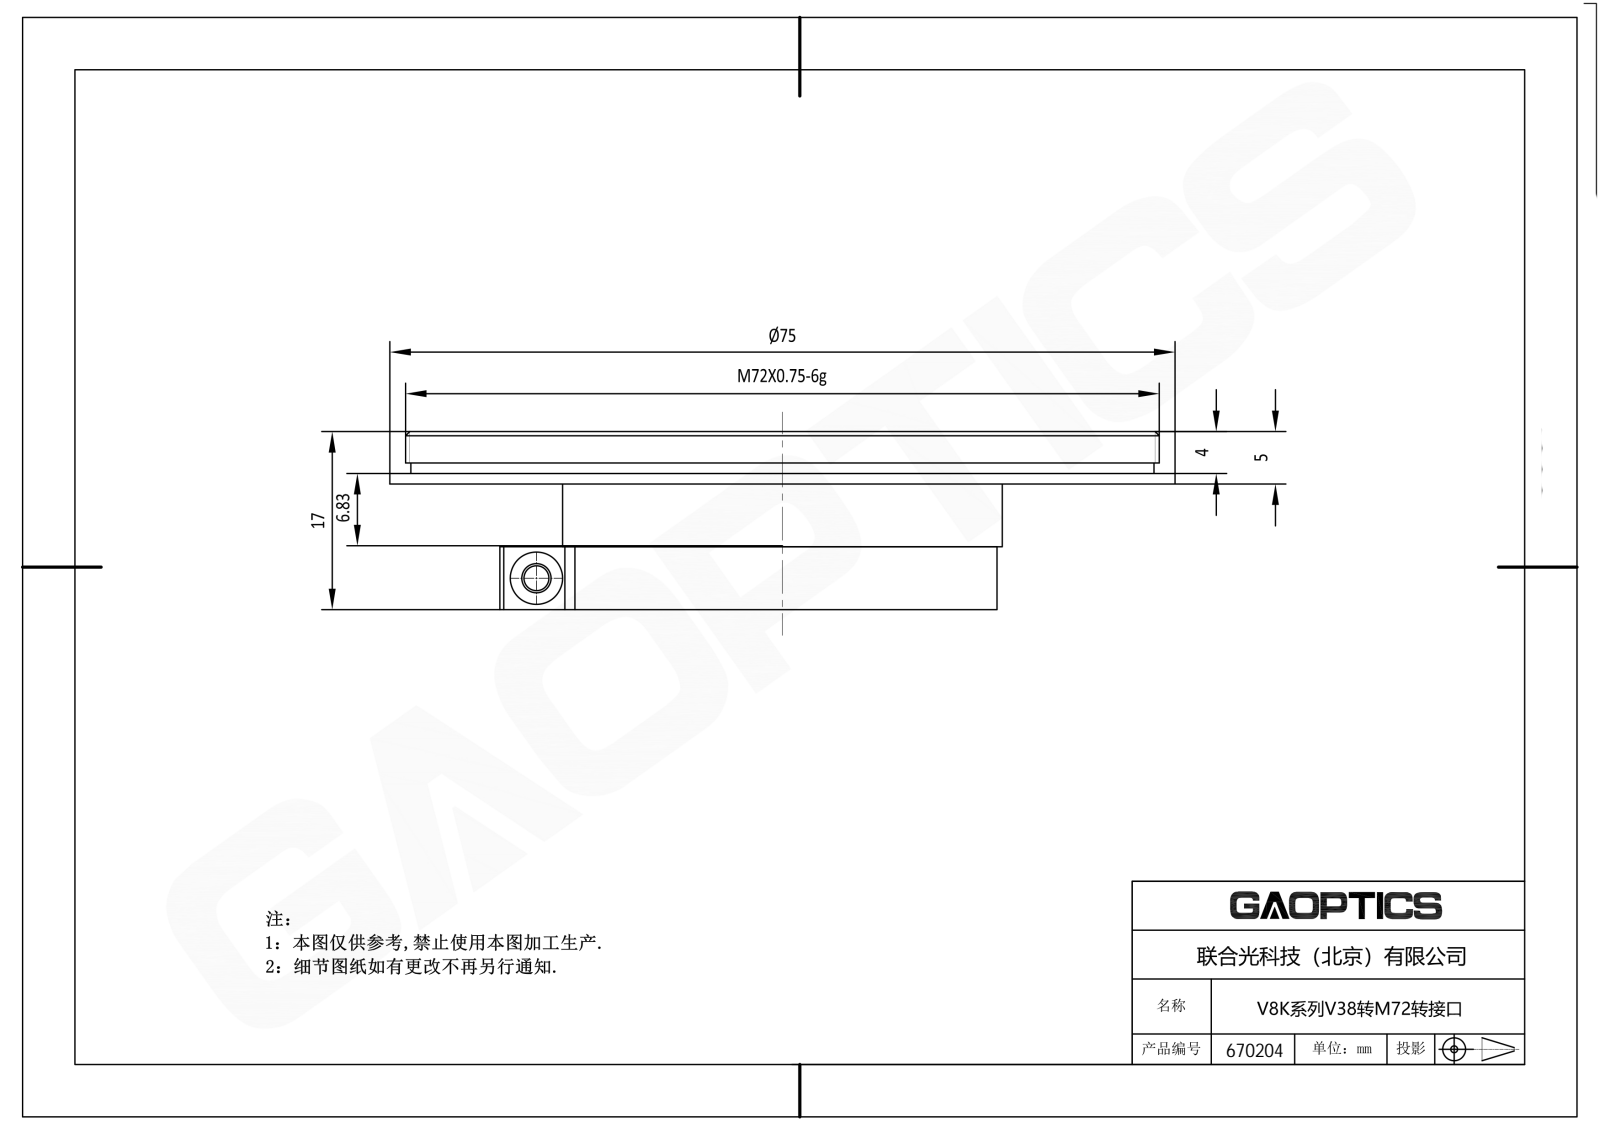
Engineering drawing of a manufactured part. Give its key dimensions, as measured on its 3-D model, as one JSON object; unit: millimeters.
{"step_written_by": "SolidWorks 2019 (CONFIG_CONTROL_DESIGN)", "units": "millimeters", "bodies": {"solids": 3, "faces": 118, "planar": 43, "cylindrical": 62, "other": 13}, "overall_size": [75, 75, 24.2], "volume_mm3": 14050, "surface_area_mm2": 20721, "round_holes": [[2.6, 3], [2.4, 1], [3.2, 1], [5, 1], [34, 1], [37.4, 1], [38, 1], [68, 1]], "round_bosses_or_shafts": [[75, 1], [72, 1], [71, 1], [44.2, 1], [42, 1], [41, 1], [40, 1], [39.5, 1]], "partial_cylinders_radius": [[1, 2], [27, 1]], "face_to_face_distances": [1, 5, 12.7, 13.7, 19.2, 6, 7, 4, 6.7, 11]}
